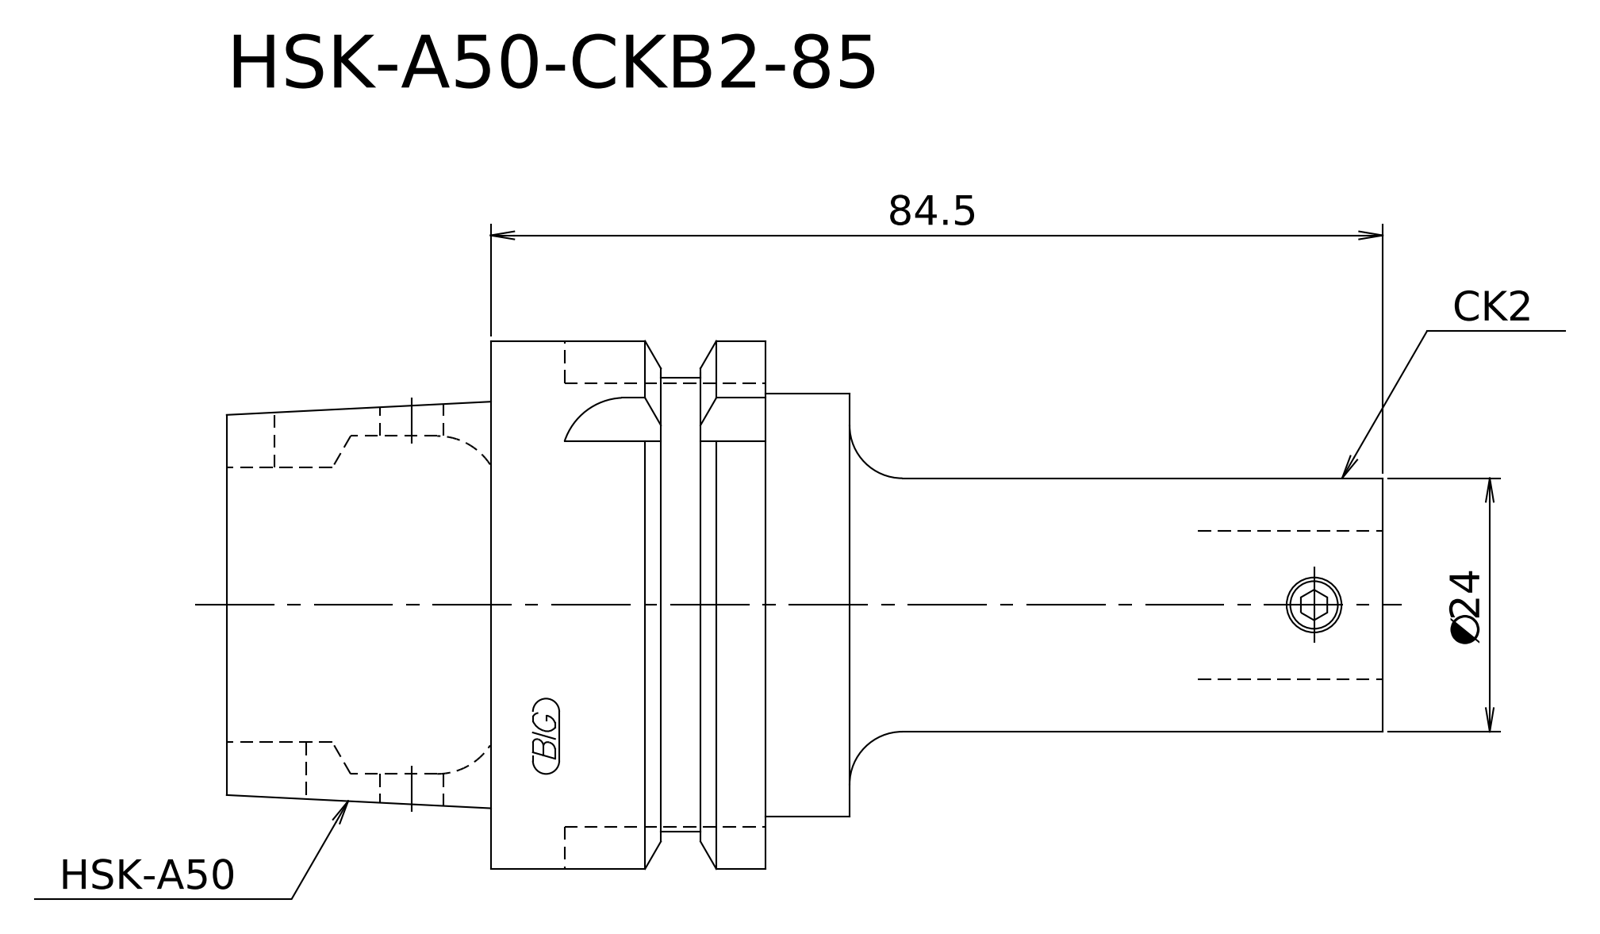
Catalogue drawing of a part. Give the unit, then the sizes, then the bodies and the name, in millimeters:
Units: millimetres
Overall size (bounding box): 109.5 × 50 × 50
Round bosses / shafts (diameter × count): ⌀50 ×1, ⌀43 ×1, ⌀40 ×1, ⌀38.3 ×1, ⌀24 ×1
Main face-to-face distances: 25, 26, 51, 58.5, 84.5, 109.5, 50.5, 8, 34, 59
Volume: 109 756 mm³ · Surface area: 16 018 mm²
Bodies: 1 solid, 17 faces (7 planar, 6 cylindrical, 4 other)
STEP written by: Kubotek KeyCreator V8.5.1 (14335) (CONFIG_CONTROL_DESIGN)
